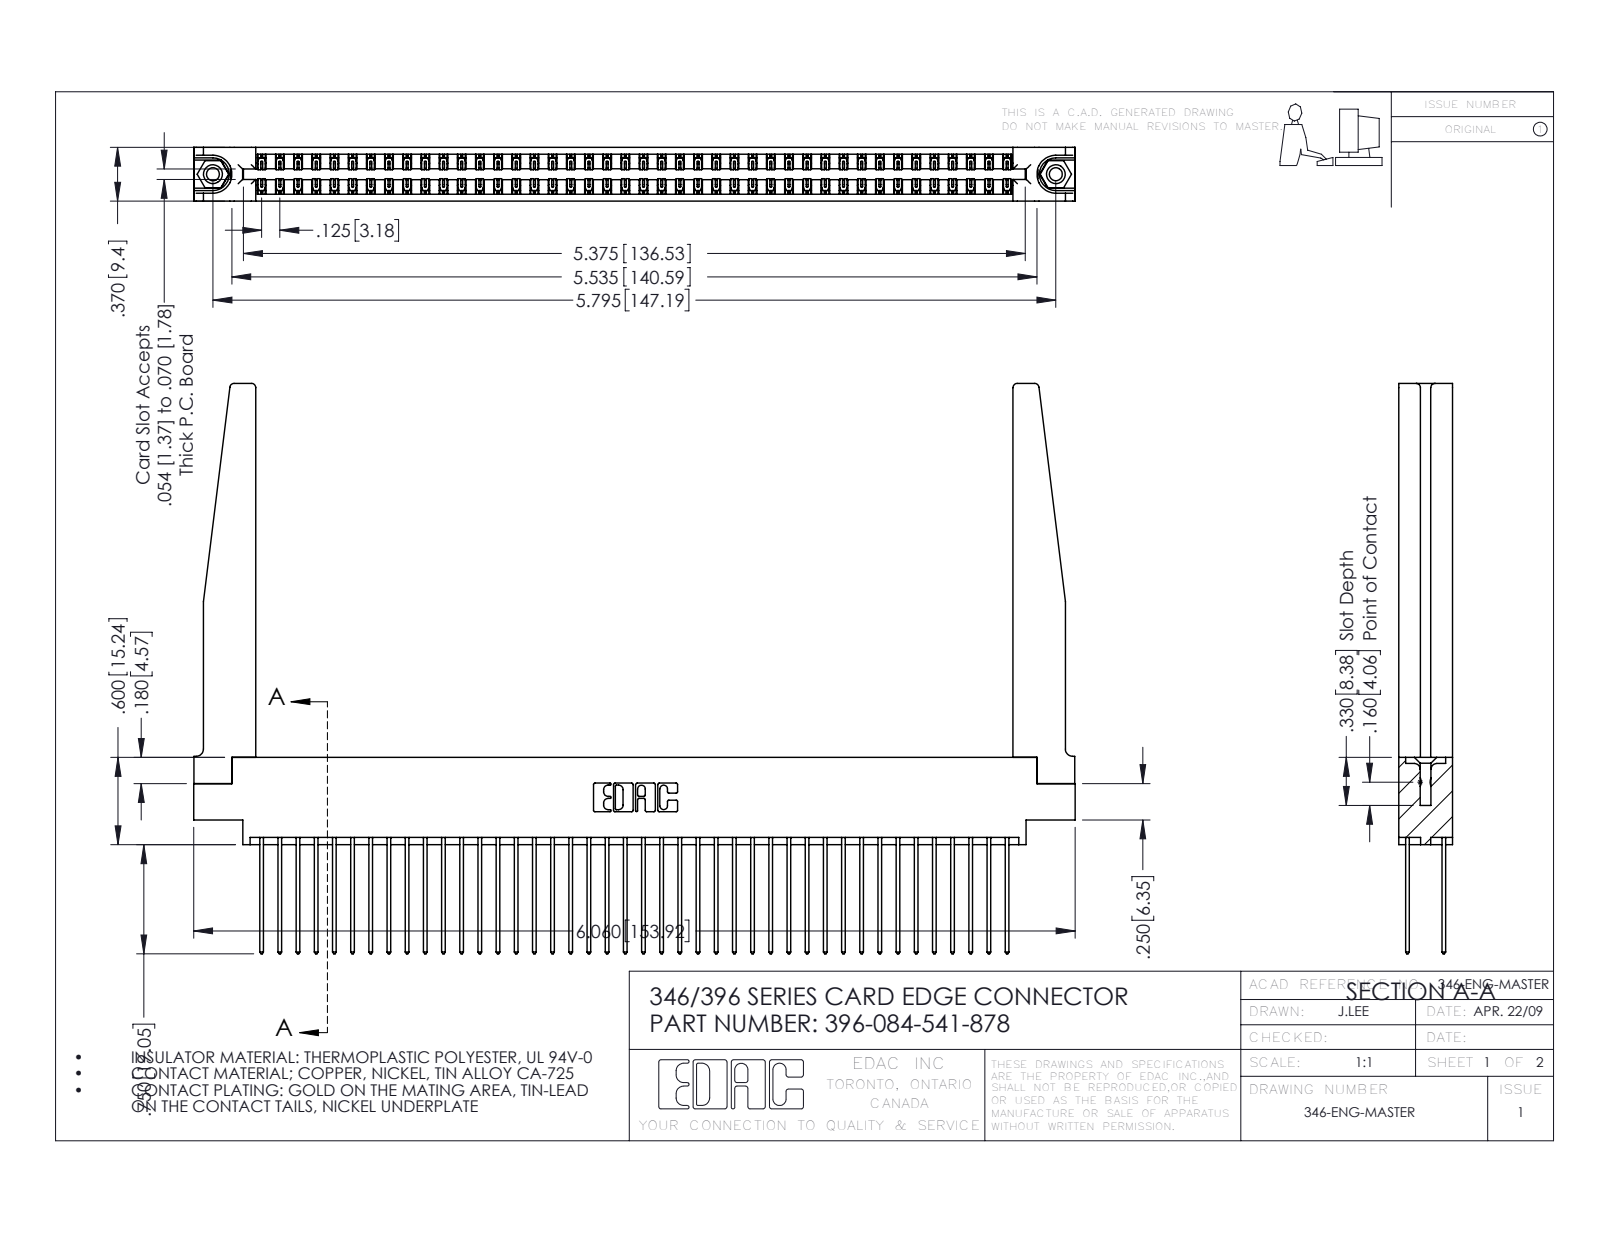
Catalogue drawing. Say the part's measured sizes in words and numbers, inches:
The part is named "346 Part_0.170 Offset - 0.156 Dia-TH; 396-084-541-878; 345-292-001_345-293-141; 345-250-001_345-250-001-102 (+1 more)". Its 3-D file was written by "SolidWorks 2016 (CONFIG_CONTROL_DESIGN)". It is 89 solids with 4728 faces: 3162 planar, 1514 cylindrical and 52 other. Overall it measures 6.06 by 3.92 by 0.37 inches. Its volume is 1.358 cubic inches and its surface area 46.67 square inches. Round holes: 2 of diameter 0.089, 2 of diameter 0.125, 2 of diameter 0.156, 1 of diameter 0.064. Round bosses or shafts: 2 of diameter 0.155. Partial cylindrical surfaces (rounded edges, fillets, slot ends): 126 of radius 0.006, 84 of radius 0.01, 22 of radius 0.01, 8 of radius 0.03, 6 of radius 0.007, 6 of radius 0.031, 3 of radius 0.026, 2 of radius 0.014. The main face-to-face distances are 0.048, 0.322, 0.37, 0.072, 0.25, 0.298, 0.025, 0.275, 0.15, 0.148. The hole center spacings are 0.246, 5.586, 5.795.
